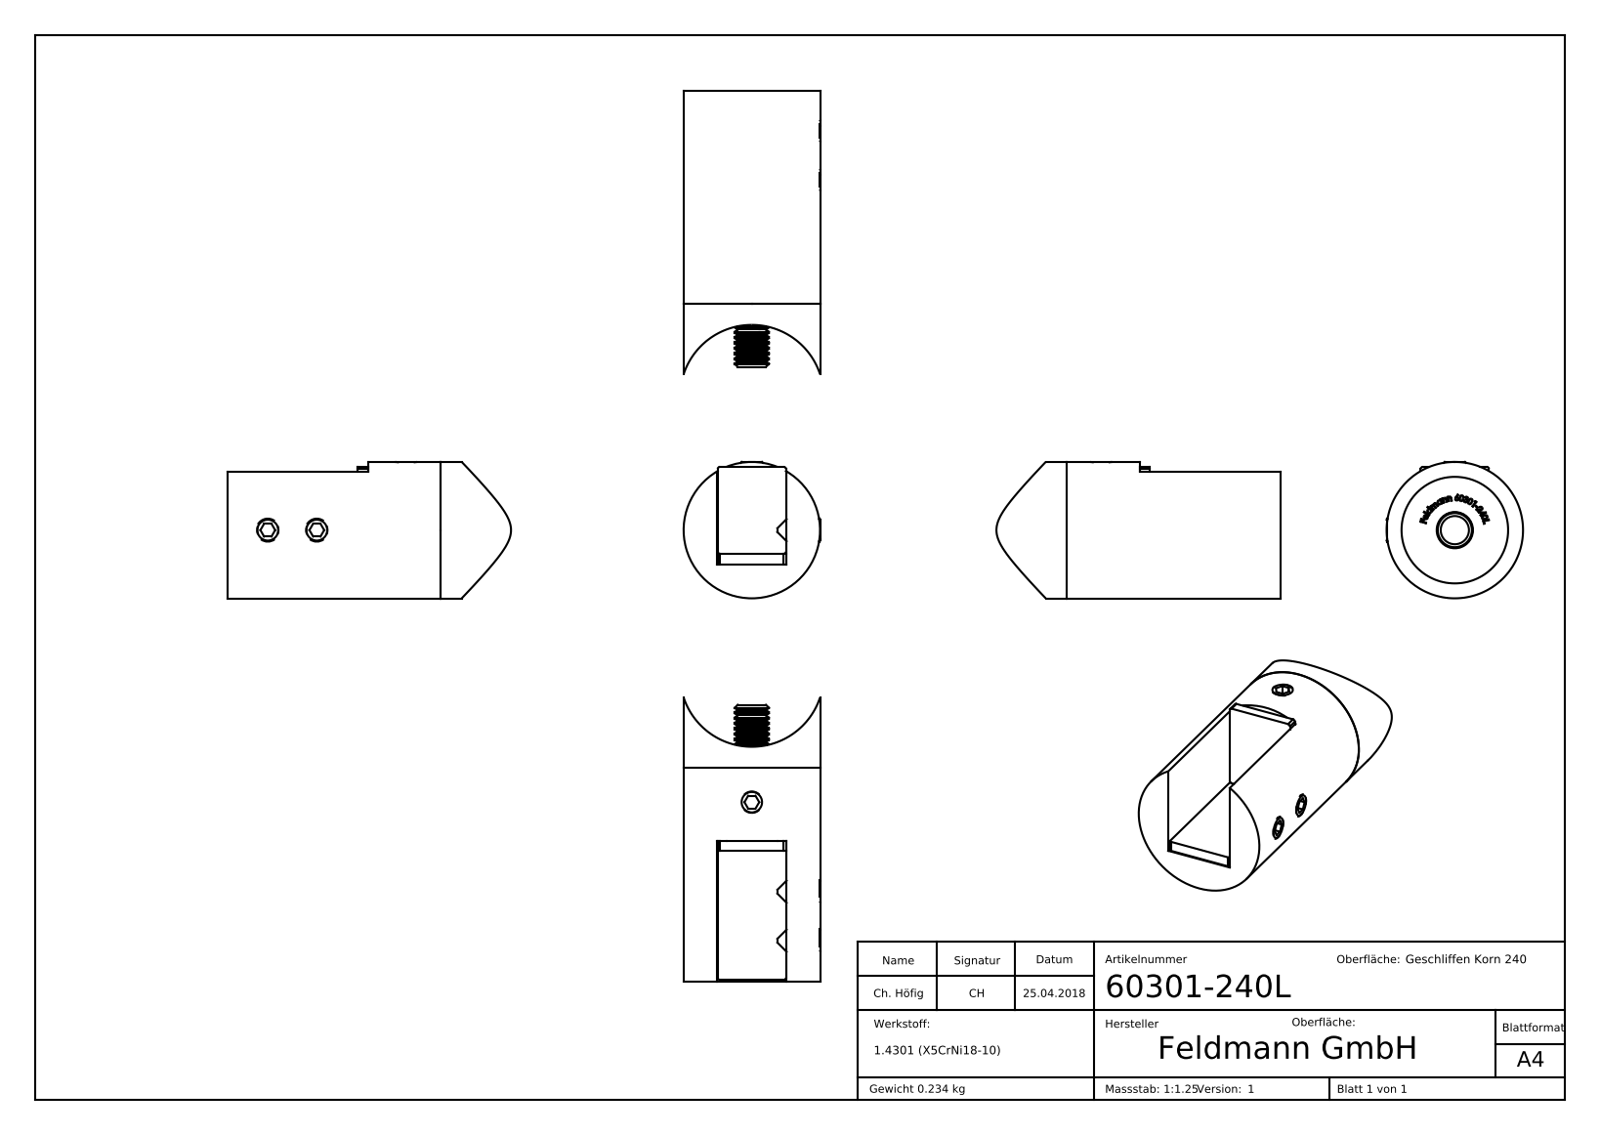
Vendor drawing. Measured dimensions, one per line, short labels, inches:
name: socket countersunk head screw_din_DIN 7991 - M8 x 25 --- 25S; 6030X-240X Teil4_60301-240L Teil4; 60301-240L; 6030X-240X Teil1 (+8 more)
written by: SolidWorks 2018 (CONFIG_CONTROL_DESIGN)
unit: in
bodies: 8 solids, 423 faces (184 planar, 53 cylindrical, 186 other)
size: 2.756 × 2.553 × 1.26
volume: 1.977 in³; area: 26.14 in²
holes: 3× ⌀0.197, 1× ⌀0.335, 1× ⌀0.984
bosses: 3× ⌀0.236, 1× ⌀1.26, 1× ⌀0.787, 1× ⌀0.613, 1× ⌀0.315
rounds: 8× R0.02, 1× R0.951
face distances: 0.096, 0.642, 0.669, 0.13, 0.799, 2.098, 1.969, 1.299, 0.896, 0.766
hole spacings: 0.453
